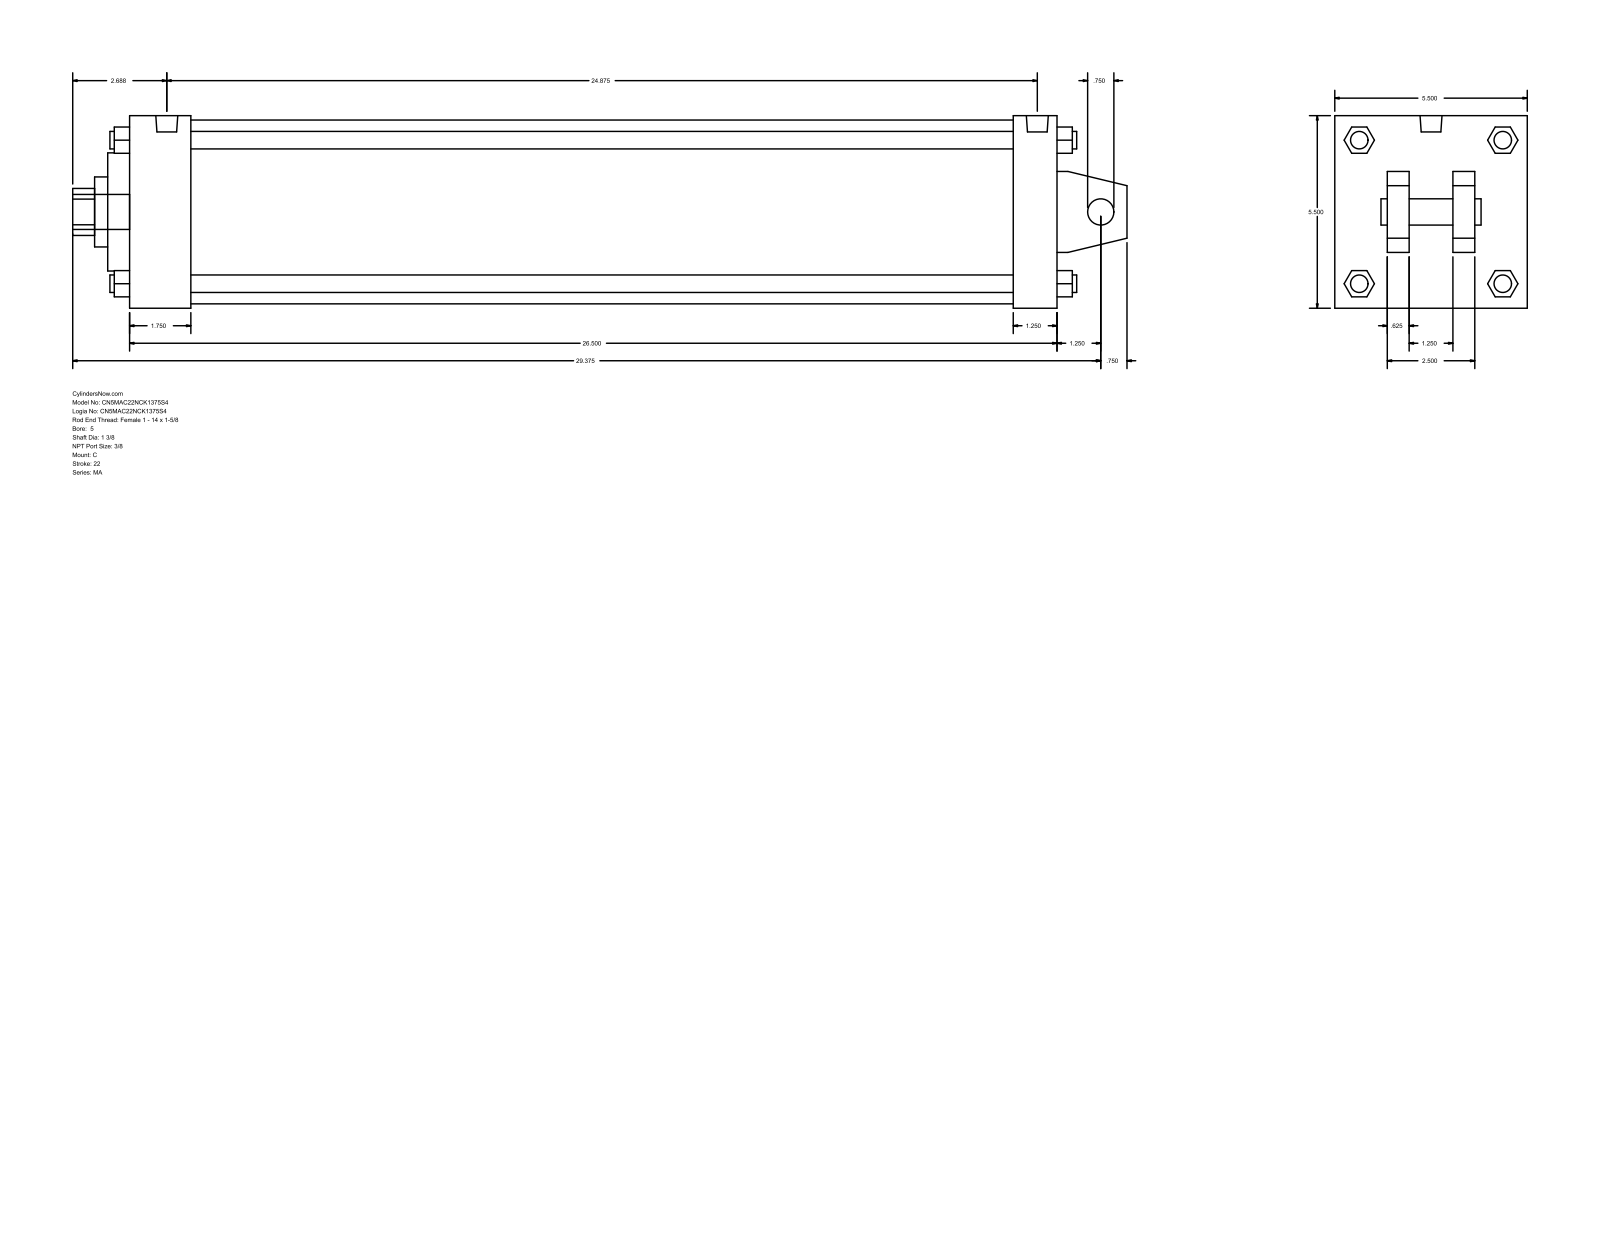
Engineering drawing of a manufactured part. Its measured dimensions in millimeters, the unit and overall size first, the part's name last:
Units: millimetres
Overall size (bounding box): 765.17 × 139.7 × 139.7
Round holes (diameter × count): ⌀19.05 ×1, ⌀34.92 ×1, ⌀50.8 ×1, ⌀85.72 ×1, ⌀133.35 ×1
Round bosses / shafts (diameter × count): ⌀12.7 ×4, ⌀11.11 ×4, ⌀15.93 ×2, ⌀25.4 ×1
Partial cylindrical surfaces — rounded edges, fillets, slot ends (radius × count): R17.06 ×1
Main face-to-face distances: 139.7, 673.11, 15.87, 31.76, 641.35, 44.45, 596.9, 628.66, 38.1, 101.6
Bodies: 0 solids, 141 faces (109 planar, 32 cylindrical, 0 other)
Part name (STEP PRODUCT): MA_C__0500_1.375
STEP written by: GSSL Pune (CONFIG_CONTROL_DESIGN)
